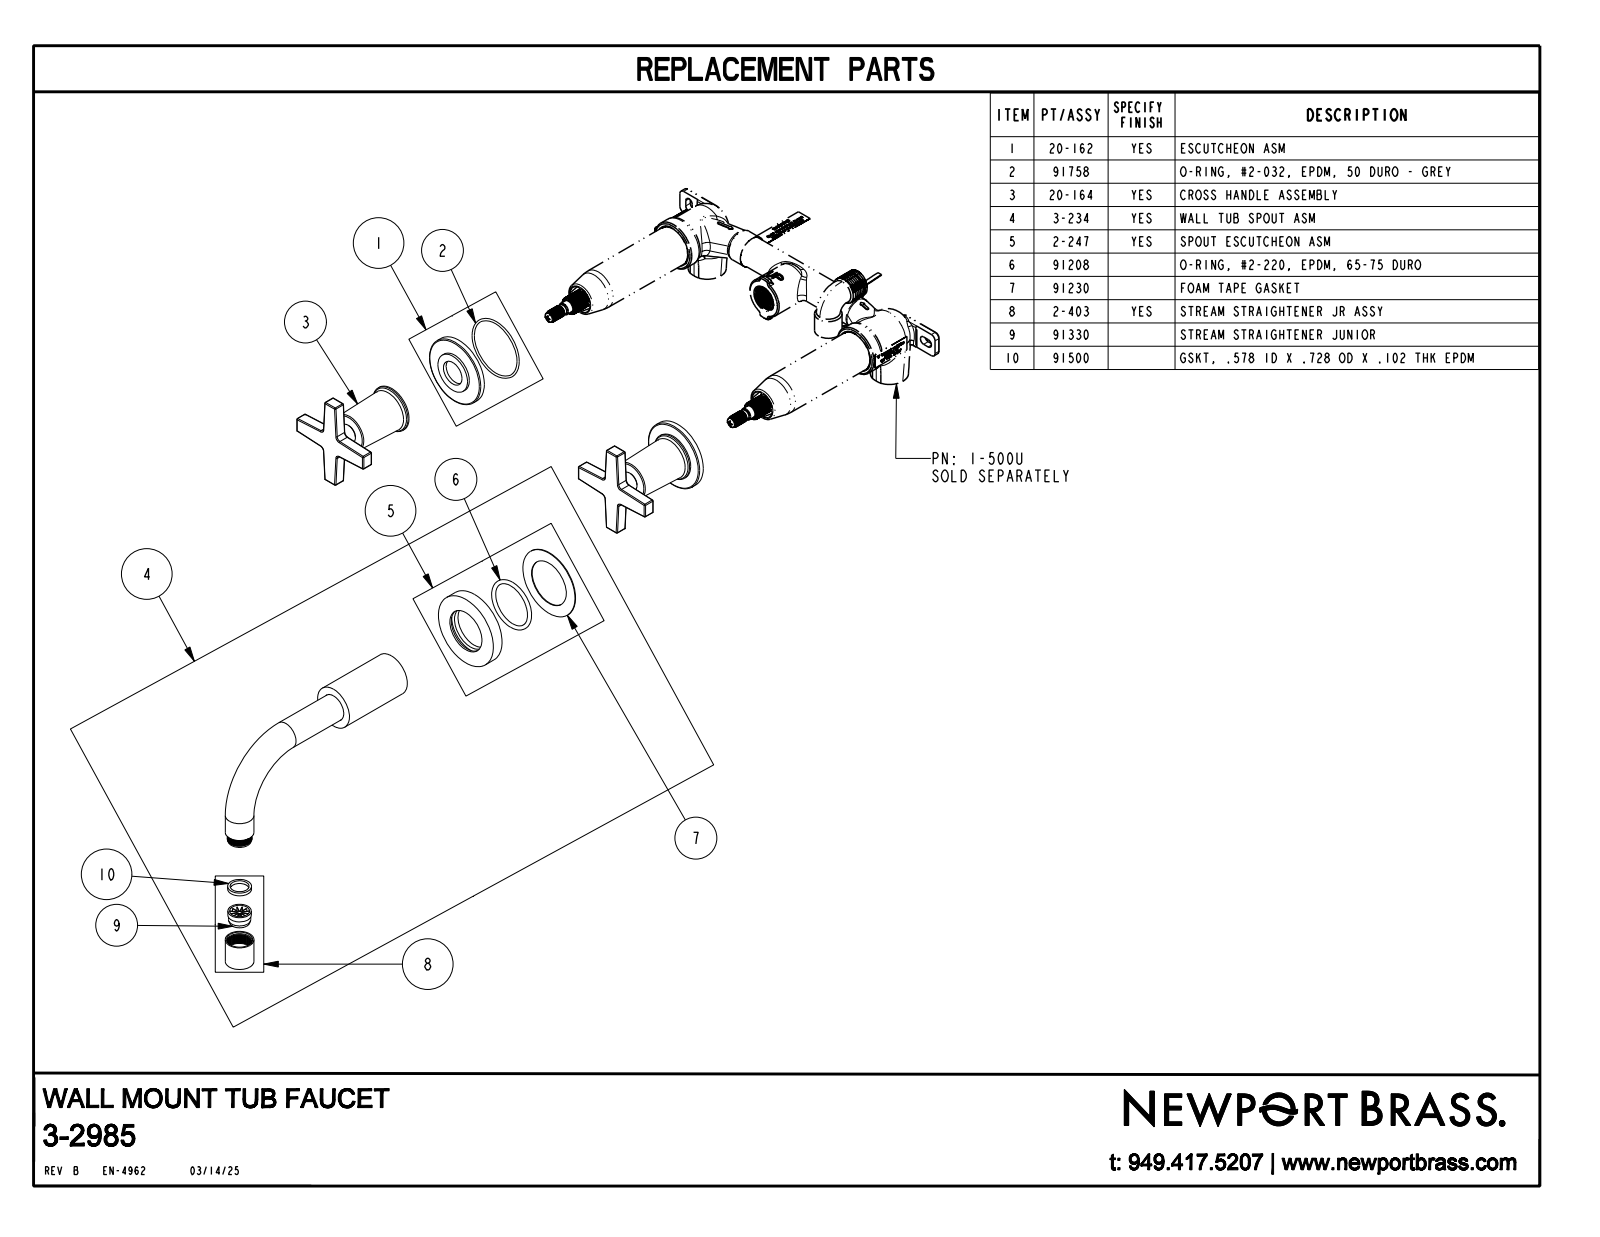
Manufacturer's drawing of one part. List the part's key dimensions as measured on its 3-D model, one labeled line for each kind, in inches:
Part name (STEP PRODUCT): 3-2985_SW0001
STEP written by: CREO PARAMETRIC BY PTC INC, 2018400 (AUTOMOTIVE_DESIGN)
Units: inches
Bodies: 3 solids, 216 faces (42 planar, 100 cylindrical, 74 other)
Overall size (bounding box): 10.883 × 10.761 × 5.998
Volume: 15.99 in³ · Surface area: 88.02 in²
Round bosses / shafts (diameter × count): ⌀2.2 ×2, ⌀1.5 ×2, ⌀1.275 ×2, ⌀0.875 ×2, ⌀0.625 ×2, ⌀0.525 ×2, ⌀2.375 ×1, ⌀1.375 ×1
Partial cylindrical surfaces — rounded edges, fillets, slot ends (radius × count): R0.03 ×60, R0.125 ×8
Main face-to-face distances: 2.87, 0.187, 2.683, 2.495, 2.308, 0.375, 0.375, 0.188, 2.12, 2.495
